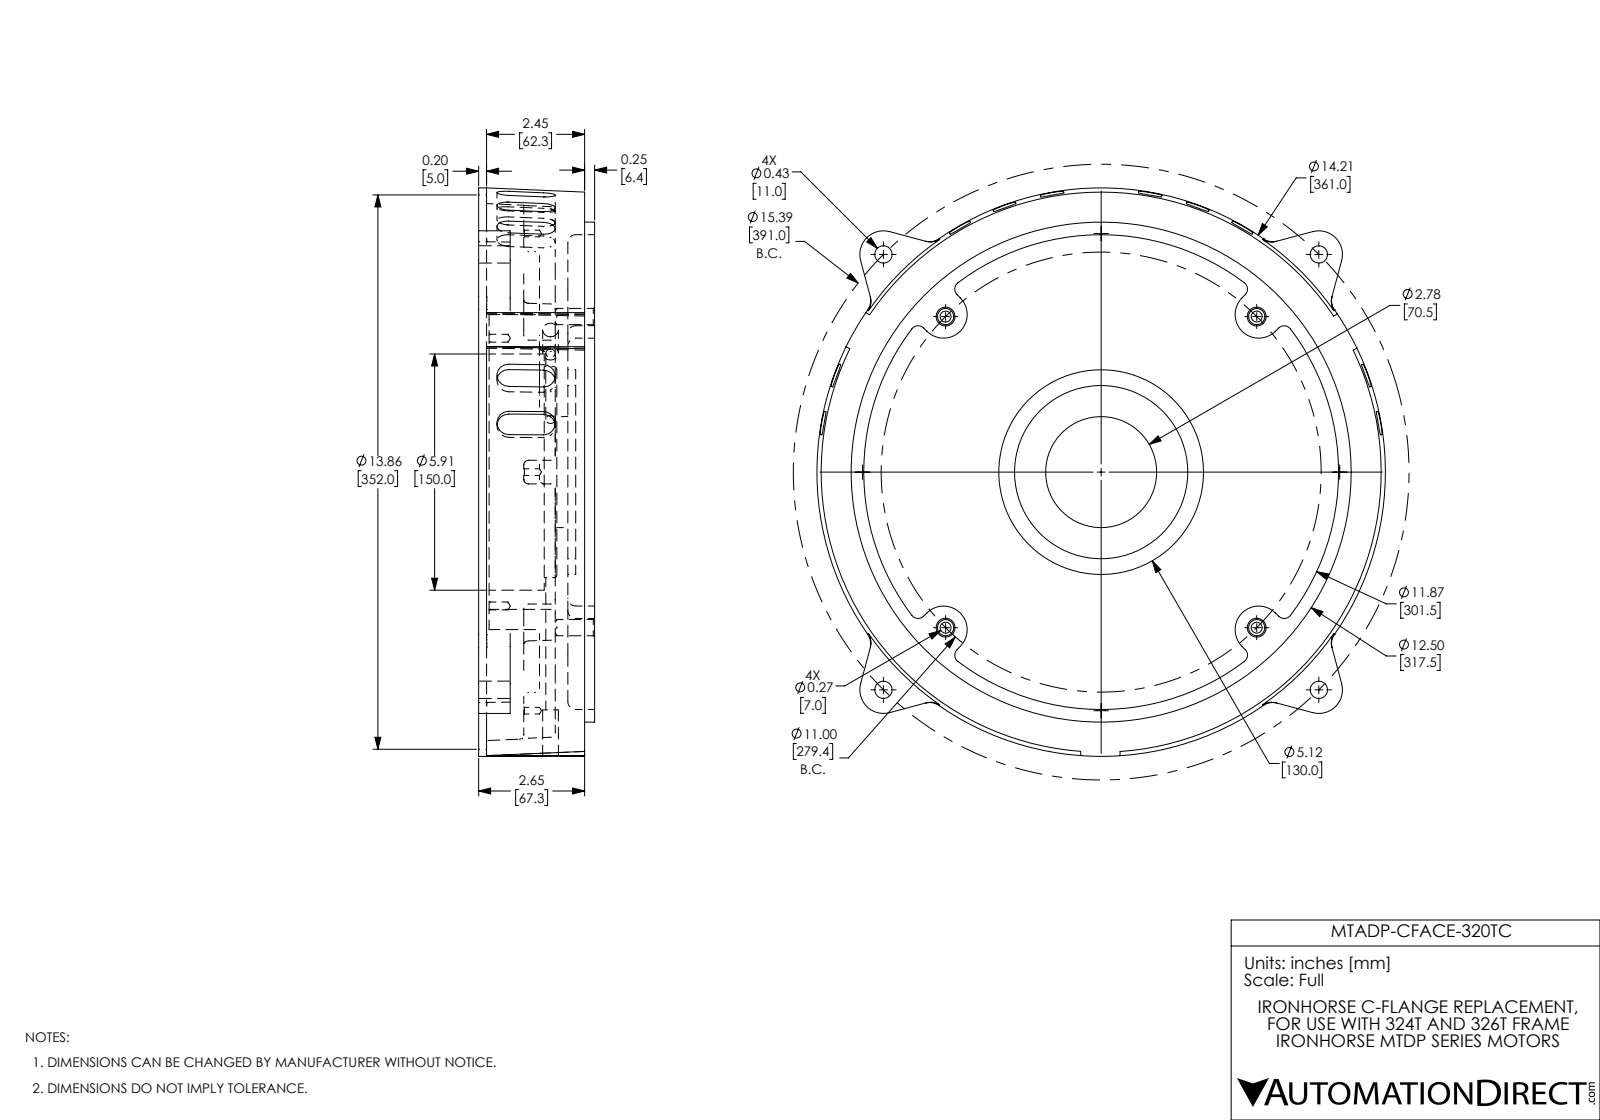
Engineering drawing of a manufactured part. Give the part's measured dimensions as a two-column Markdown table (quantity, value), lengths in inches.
| quantity | value |
| --- | --- |
| part name | MTADP-CFACE-320 |
| STEP written by | SolidWorks 2017 (AUTOMOTIVE_DESIGN) |
| units | inches |
| bodies | 1 solid, 561 faces (106 planar, 211 cylindrical, 244 other) |
| overall size | 14.213 × 14.213 × 2.898 |
| volume | 133.8 in³ |
| surface area | 655.7 in² |
| round holes (diameter × count) | 0.165 × 4, 0.406 × 4, 0.433 × 4, 0.197 × 2, 0.236 × 2, 0.394 × 2, 2.776 × 1, 4.331 × 1, 5.276 × 1, 5.906 × 1, 11.87 × 1, 13.858 × 1 |
| round bosses / shafts (diameter × count) | 12.5 × 1, 6.89 × 1, 5.118 × 1 |
| partial cylindrical surfaces (radius × count) | 0.118 × 63, 0.295 × 20, 0.197 × 15, 0.591 × 12, 0.394 × 8, 3.937 × 1, 7.106 × 1 |
| main face-to-face distances | 0.315, 0.734, 0.419, 0.276, 2.228, 0.591, 0.787, 0.984, 0.669, 0.25 |
| hole center spacings | 4.408, 5.467, 9.46, 10.593, 12.639, 2.197, 3.927, 5.5 |
